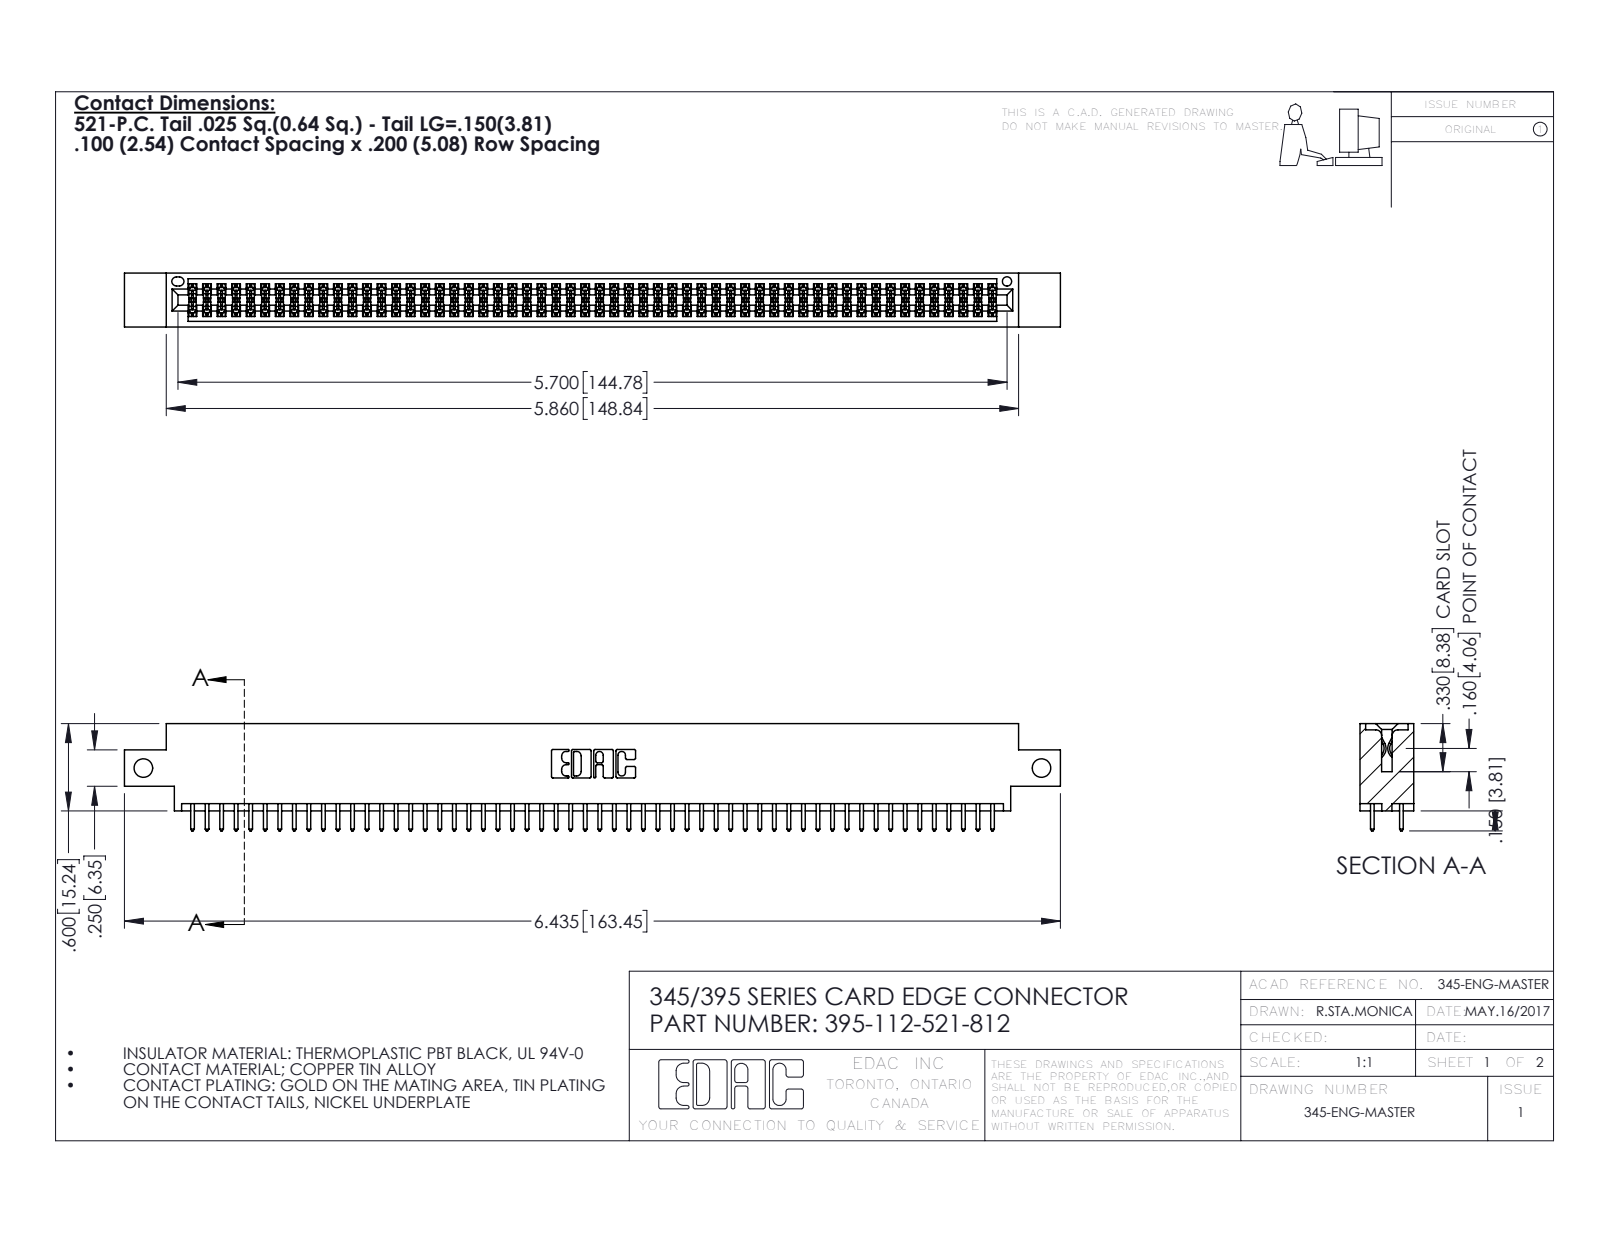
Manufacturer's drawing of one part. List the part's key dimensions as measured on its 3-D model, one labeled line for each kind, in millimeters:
Part name (STEP PRODUCT): 395-112-521-812; 345 Part_0.170 Offset - Side Mount; 345-292-001_345-293-121
STEP written by: SolidWorks 2016 (CONFIG_CONTROL_DESIGN)
Units: millimetres
Bodies: 113 solids, 5730 faces (3780 planar, 1950 cylindrical, 0 other)
Overall size (bounding box): 163.4 × 18.7 × 9.4
Volume: 15 800 mm³ · Surface area: 23 280 mm²
Round holes (diameter × count): ⌀3.3 ×2, ⌀1.6 ×1
Partial cylindrical surfaces — rounded edges, fillets, slot ends (radius × count): R0.2 ×168, R0.3 ×112, R0.3 ×22, R0.2 ×6, R0.8 ×6, R0.7 ×3, R0.4 ×2, R0.5 ×2
Main face-to-face distances: 1.8, 7.6, 9.4, 5.1, 2.5, 6.9, 0.6, 5.7, 4.4, 3.8
Hole centre spacings: 156.8
